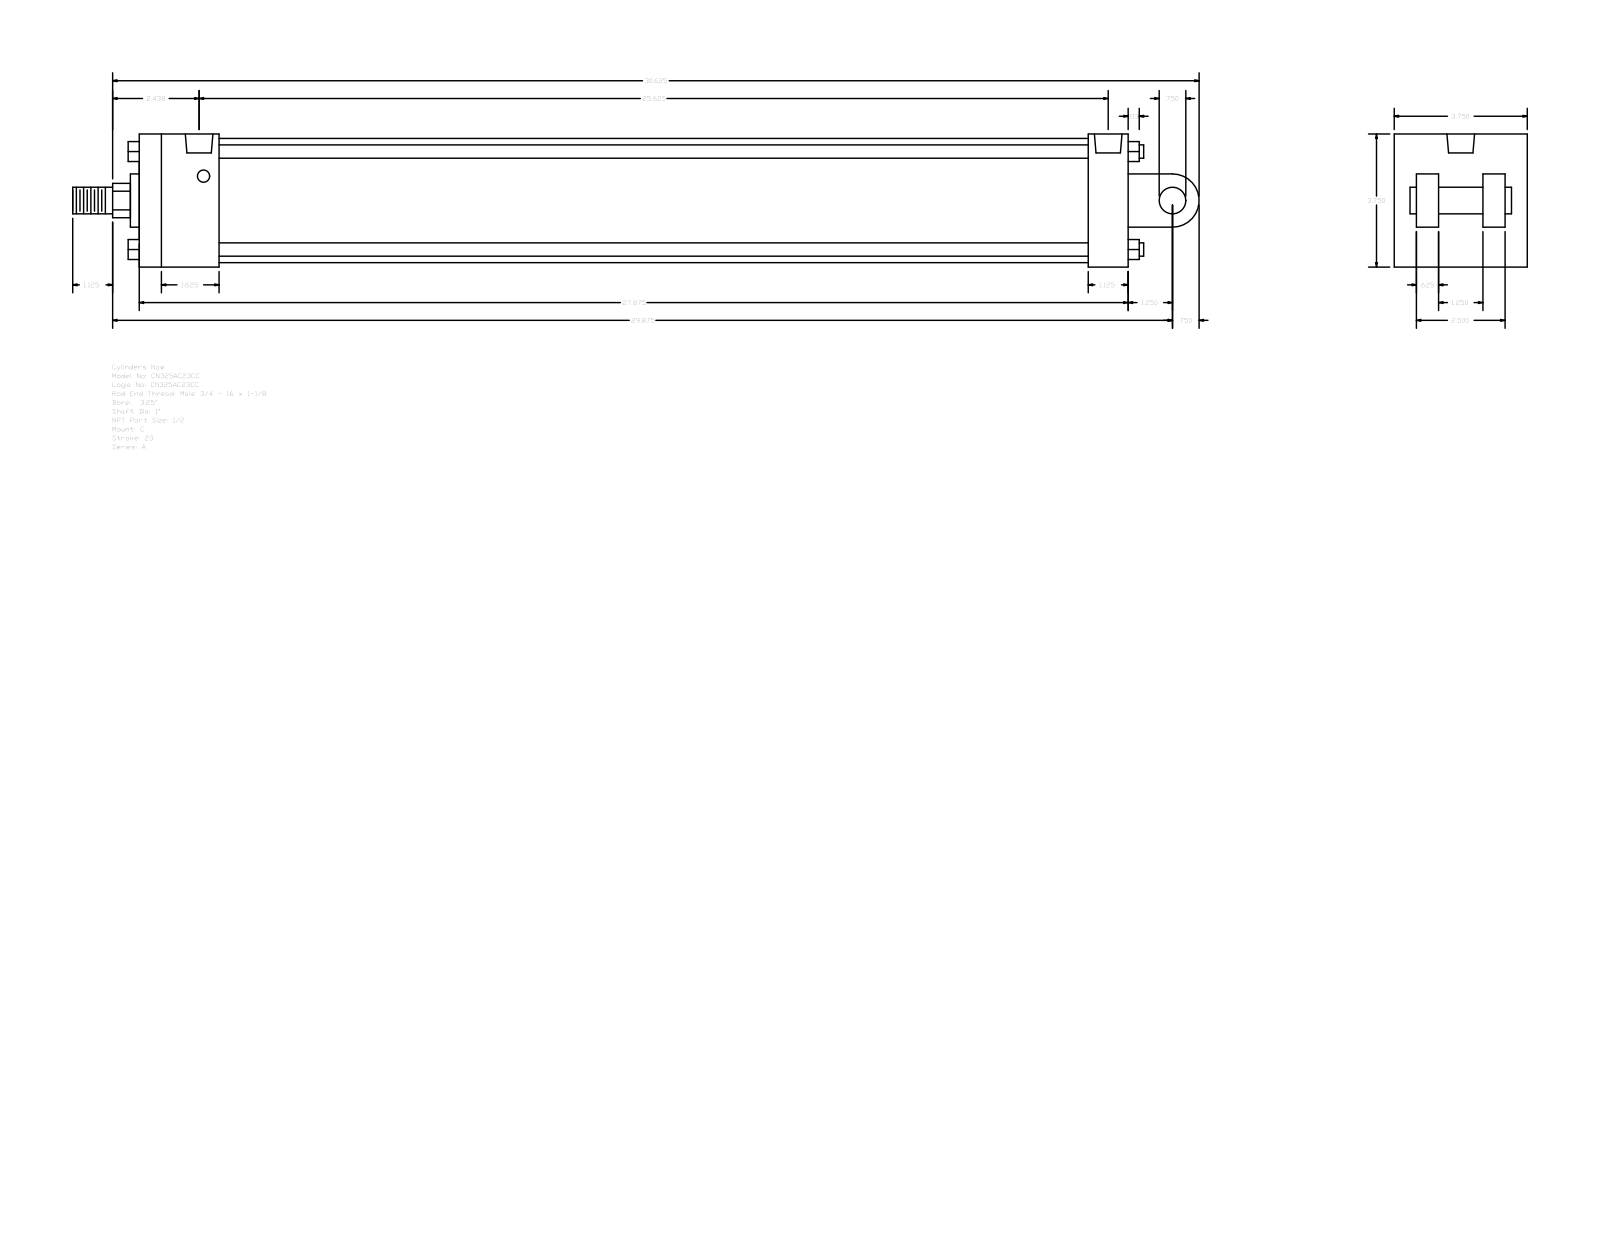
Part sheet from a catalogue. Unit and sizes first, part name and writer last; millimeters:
Units: millimetres
Overall size (bounding box): 806.45 × 95.25 × 95.25
Round holes (diameter × count): ⌀8.73 ×4, ⌀19.77 ×2
Round bosses / shafts (diameter × count): ⌀9.53 ×4, ⌀19.05 ×2, ⌀88.9 ×1, ⌀38.1 ×1, ⌀25.4 ×1
Partial cylindrical surfaces — rounded edges, fillets, slot ends (radius × count): R12.29 ×1, R19.05 ×1
Main face-to-face distances: 95.24, 708.03, 15.87, 63.5, 31.74, 79.37, 47.63, 66.67, 679.45, 28.58
Hole centre spacings: 3.18, 644.52, 647.7, 650.88
Bodies: 0 solids, 135 faces (102 planar, 33 cylindrical, 0 other)
Part name (STEP PRODUCT): A_C__0325_1
STEP written by: GSSL Pune (CONFIG_CONTROL_DESIGN)
